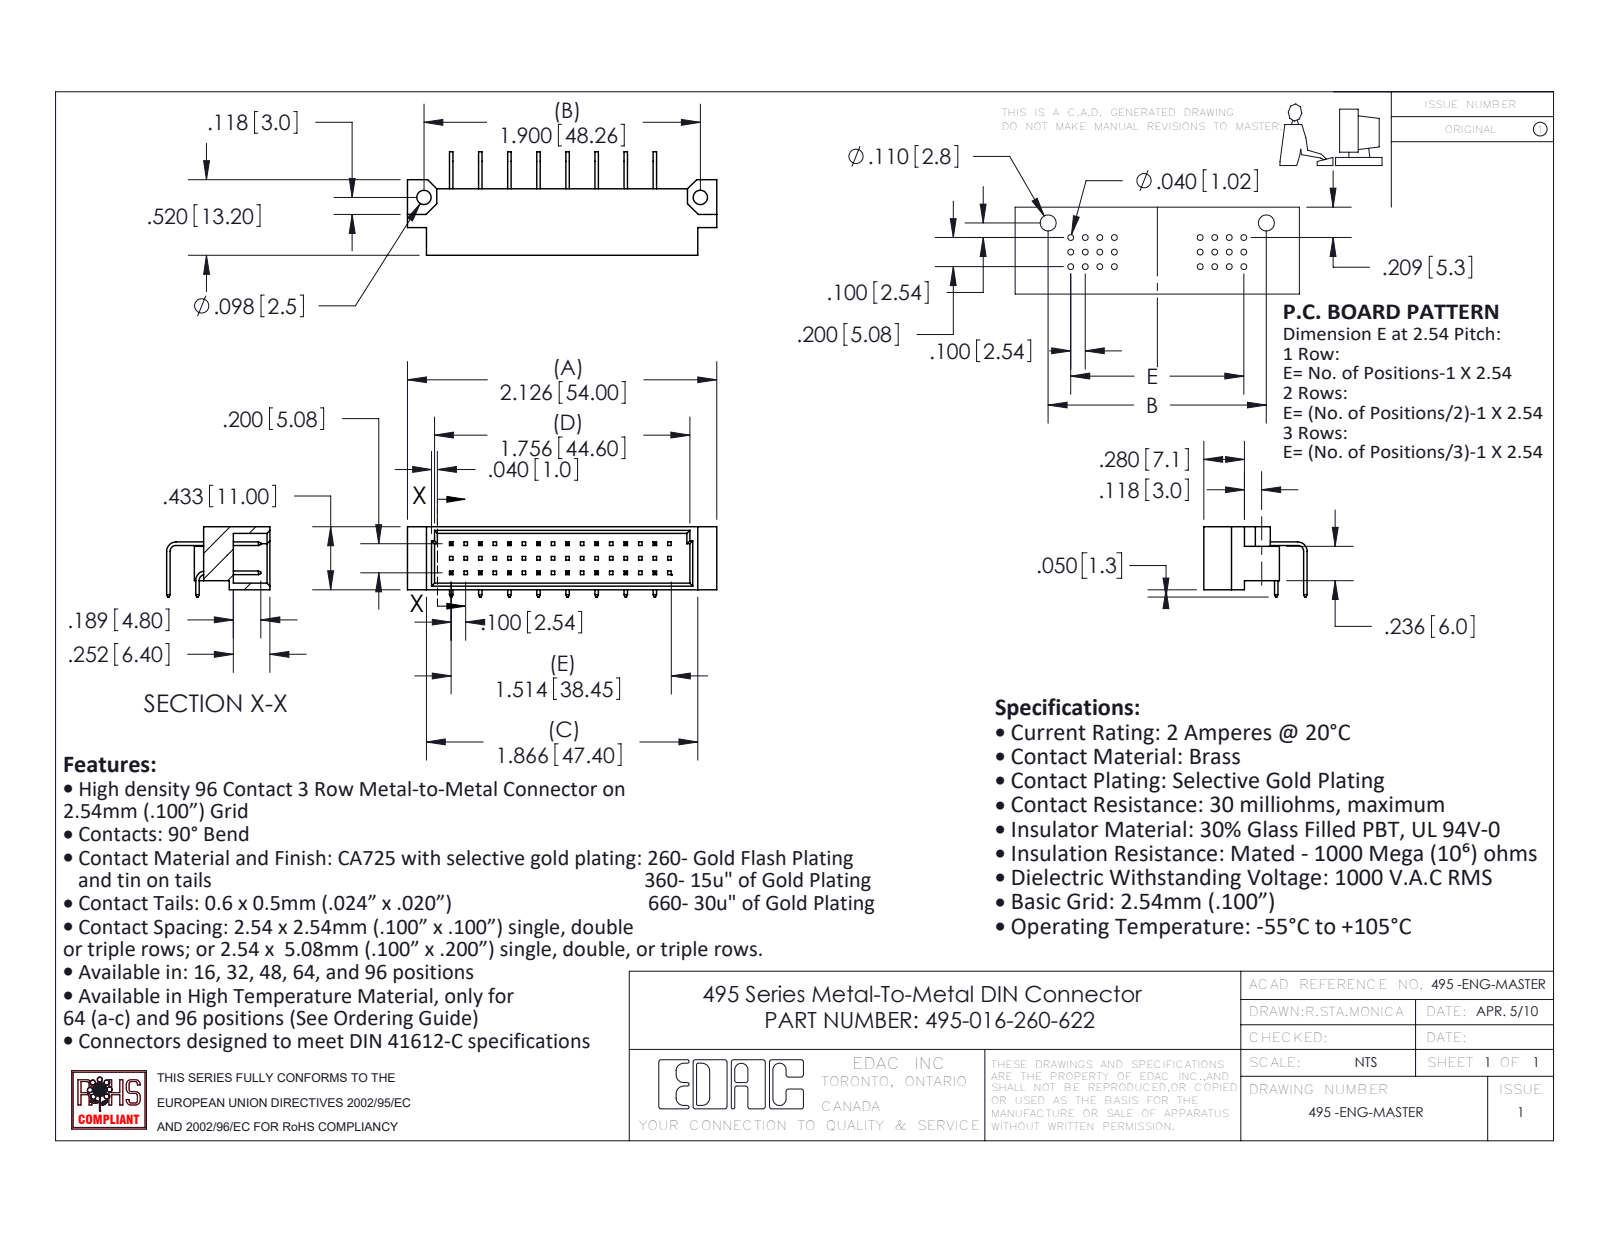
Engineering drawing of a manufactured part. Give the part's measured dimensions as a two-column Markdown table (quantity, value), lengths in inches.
| quantity | value |
| --- | --- |
| part name | 495-290-1; 495 Part_48; 495-016-260-622; 495-290-3 |
| STEP written by | SolidWorks 2020 (AUTOMOTIVE_DESIGN) |
| units | inches |
| bodies | 17 solids, 530 faces (494 planar, 36 cylindrical, 0 other) |
| overall size | 2.126 × 0.711 × 0.483 |
| volume | 0.218 in³ |
| surface area | 7.33 in² |
| round holes (diameter × count) | 0.098 × 2 |
| partial cylindrical surfaces (radius × count) | 0.04 × 2, 0.065 × 2 |
| main face-to-face distances | 0.2, 0.045, 0.388, 0.205, 0.433, 0.024, 0.6, 0.063, 0.4, 0.343 |
| hole center spacings | 1.9 |
